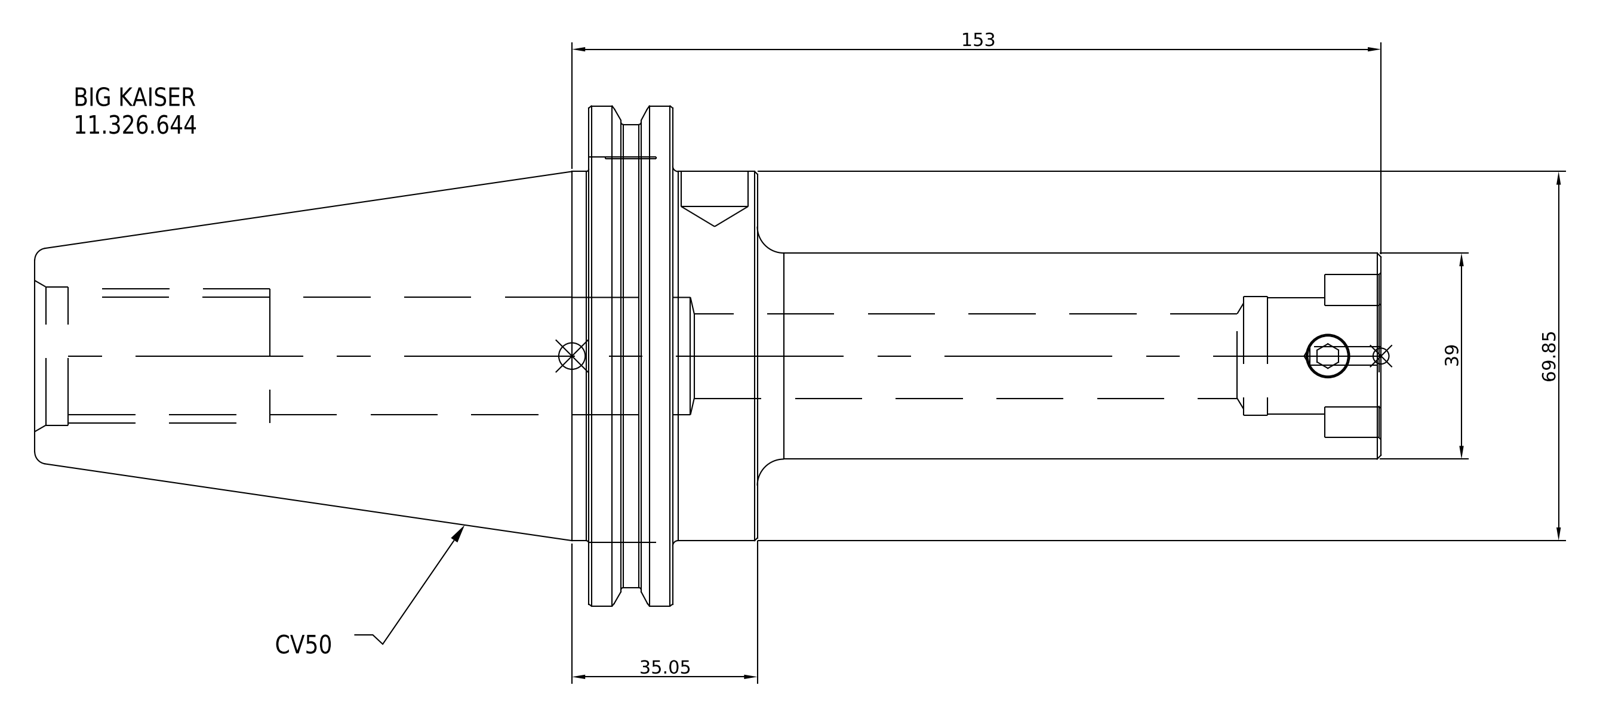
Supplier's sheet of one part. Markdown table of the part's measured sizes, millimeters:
| quantity | value |
| --- | --- |
| part name | 11.326.644 |
| STEP written by | SolidWorks 2021 (CONFIG_CONTROL_DESIGN) |
| units | millimeters |
| bodies | 1 solid, 16 faces (7 planar, 6 cylindrical, 3 other) |
| overall size | 254.6 × 98.43 × 98.43 |
| volume | 583 442 mm³ |
| surface area | 55 431 mm² |
| round bosses / shafts (diameter × count) | 98.43 × 1, 91.29 × 1, 69.85 × 1, 39 × 1 |
| main face-to-face distances | 17.55, 15.95, 33.5, 136.6, 120.65, 103.1, 118, 133.95, 151.5, 254.6 |
